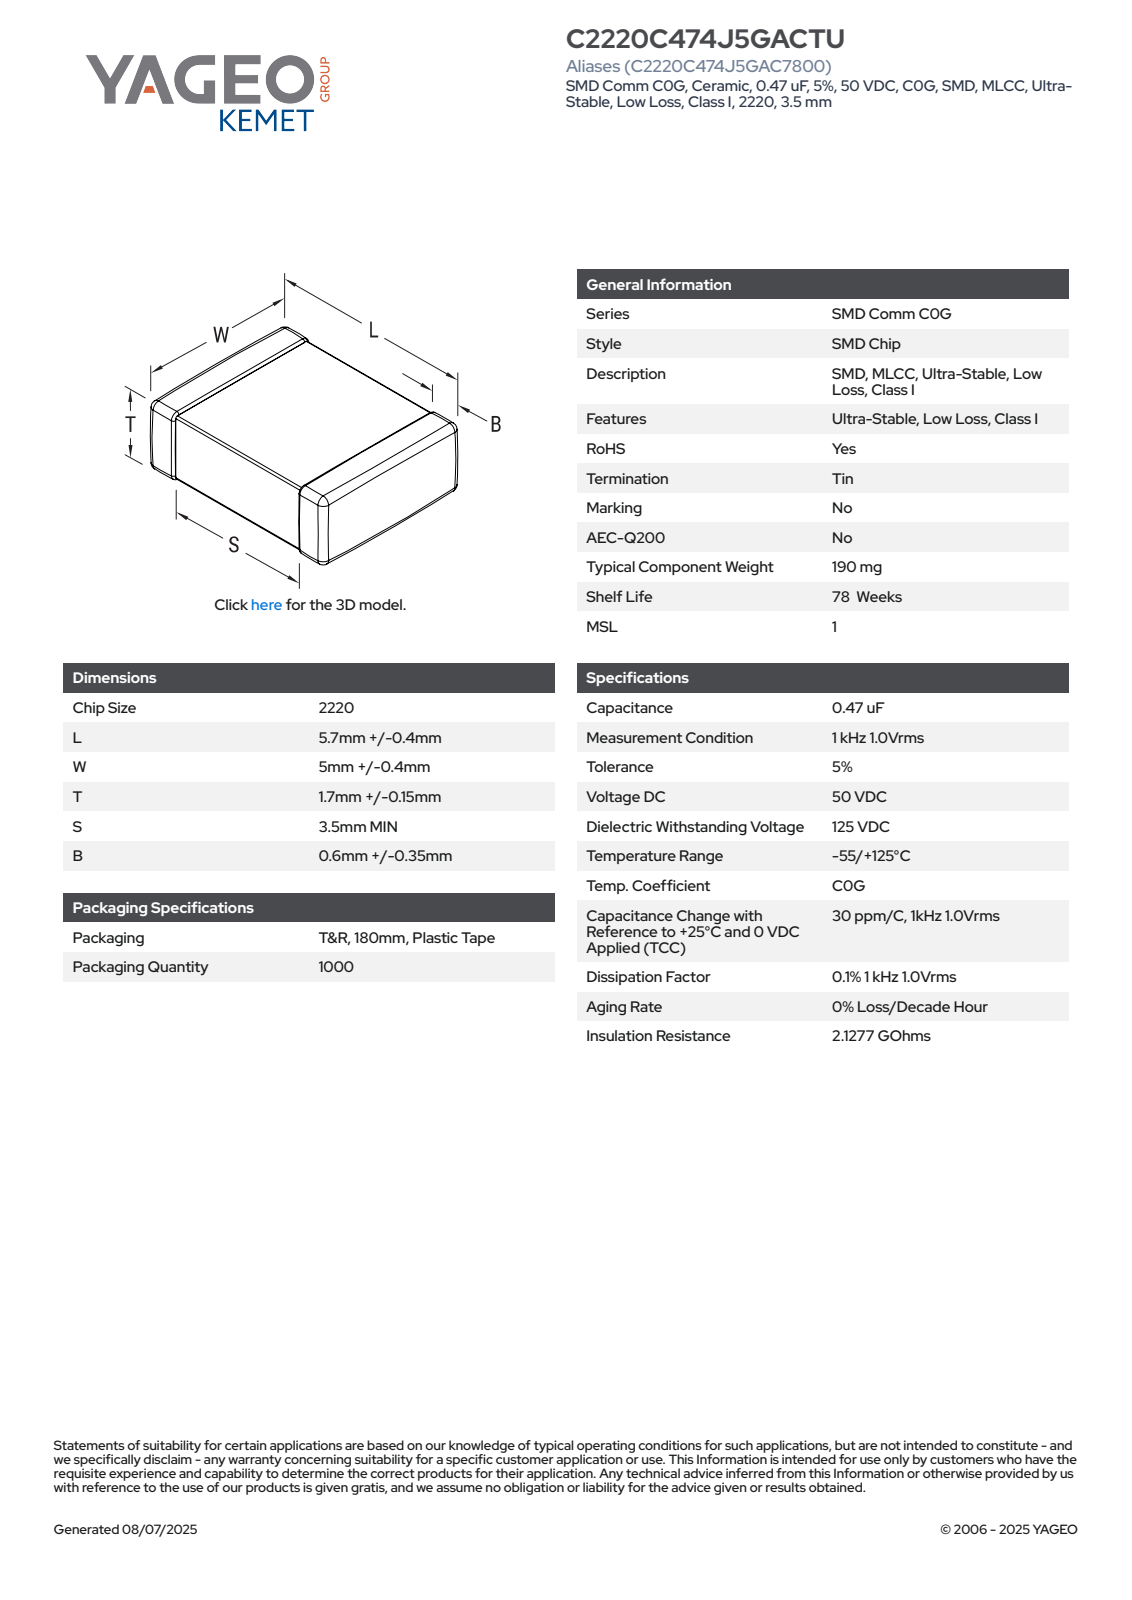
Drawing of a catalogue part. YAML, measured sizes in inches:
part_name: "CCS_CCSTD_2220_L6.1W5.4T1.85B0.6"
step_written_by: "SolidWorks 2021 (AUTOMOTIVE_DESIGN)"
units: inches
bodies: {solids: 4, faces: 125, planar: 71, cylindrical: 38, other: 16}
overall_size: [0.24, 0.213, 0.073]
volume: 0.003
surface_area: 0.167
partial_cylinders:
  - {radius: 0.004, count: 24}
face_to_face_distances: [0.064, 0.069, 0.24, 0.073, 0.204, 0.208, 0.213, 0.098, 0.142, 0.13]
